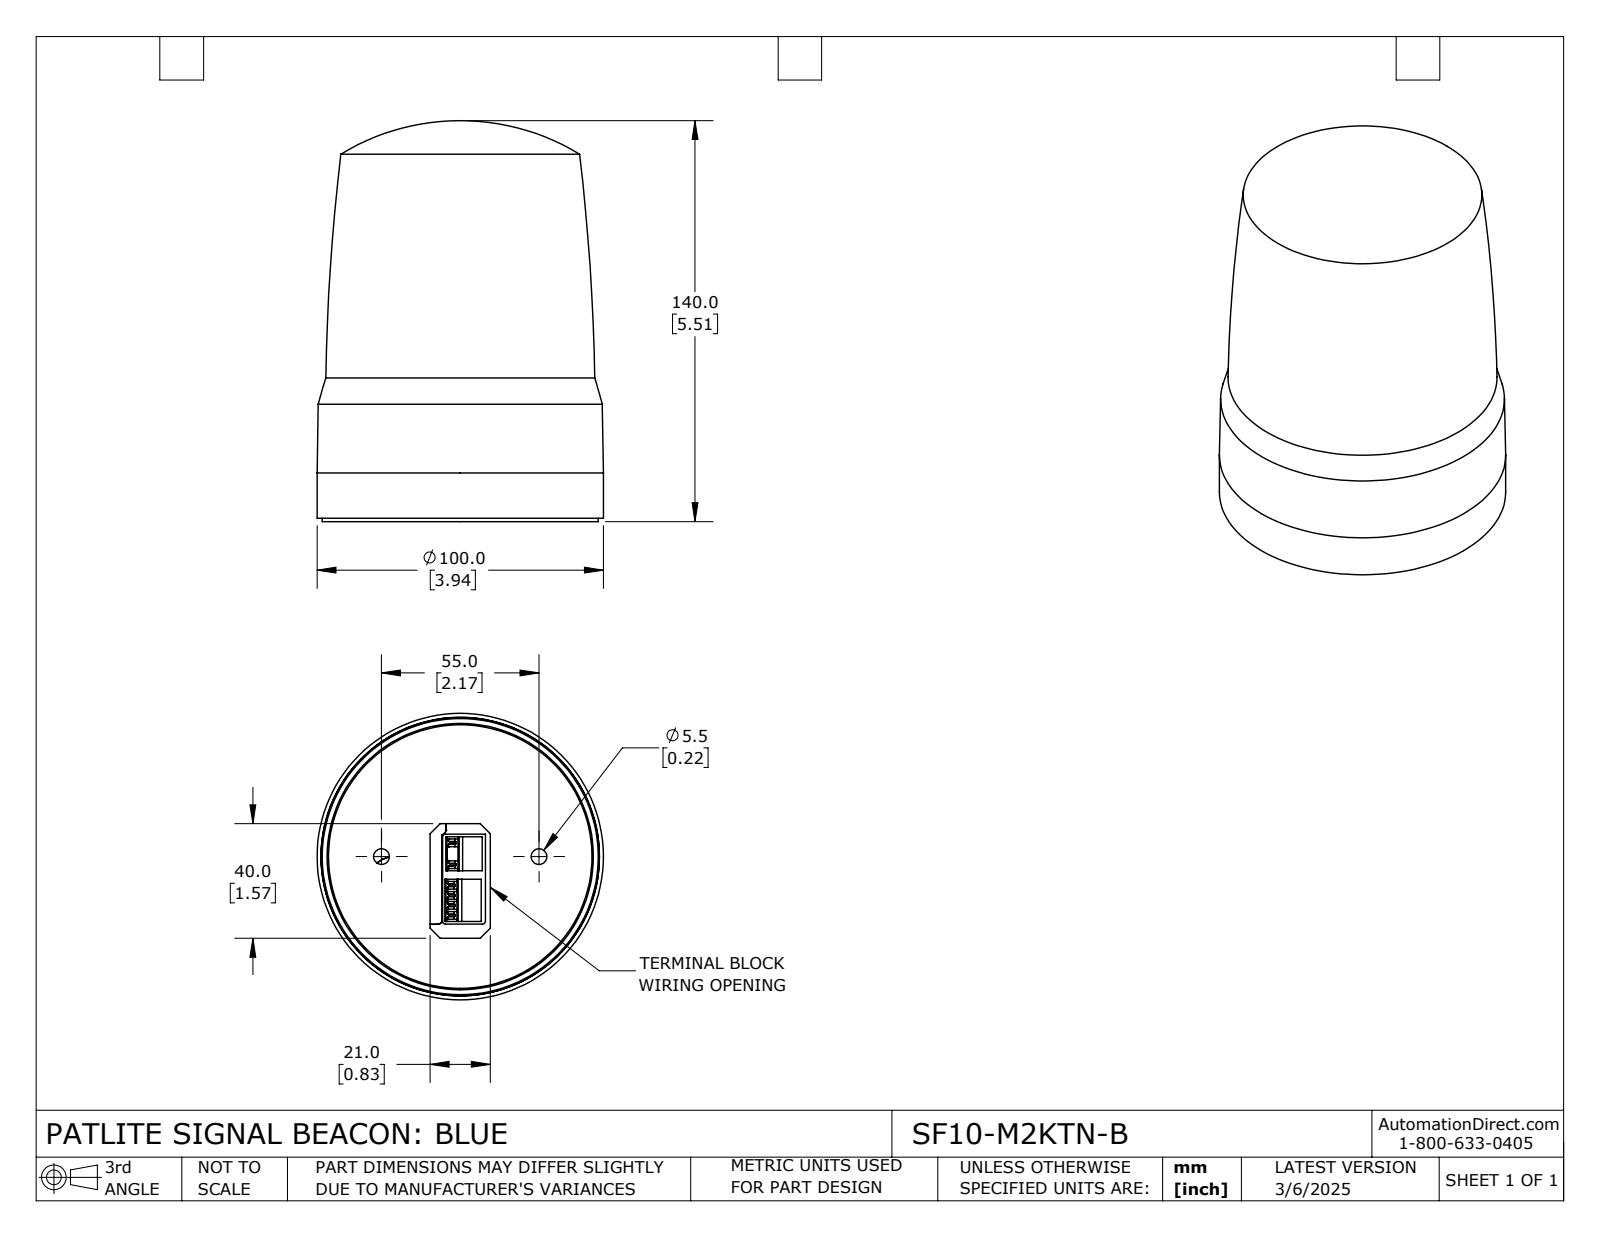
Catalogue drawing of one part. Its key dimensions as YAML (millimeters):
part_name: "SF10-M2KTN-B"
step_written_by: "SolidWorks 2024 (CONFIG_CONTROL_DESIGN)"
units: millimeters
bodies: {solids: 2, faces: 268, planar: 183, cylindrical: 29, other: 56}
overall_size: [140, 100, 100]
volume: 857676
surface_area: 76986
round_holes:
  - {diameter: 5.5, count: 2}
  - {diameter: 13, count: 2}
  - {diameter: 93, count: 1}
  - {diameter: 95.6, count: 1}
round_bosses_or_shafts:
  - {diameter: 100, count: 1}
  - {diameter: 96.4, count: 1}
  - {diameter: 94.5, count: 1}
  - {diameter: 93.2, count: 1}
  - {diameter: 92, count: 1}
partial_cylinders:
  - {radius: 0.3, count: 2}
  - {radius: 44.32, count: 1}
  - {radius: 44.75, count: 1}
face_to_face_distances: [6.3, 14.7, 8.4, 1.5, 6.9, 13.2, 12.6, 3.15, 4.4, 7]
hole_center_spacings: [27.5, 55]
